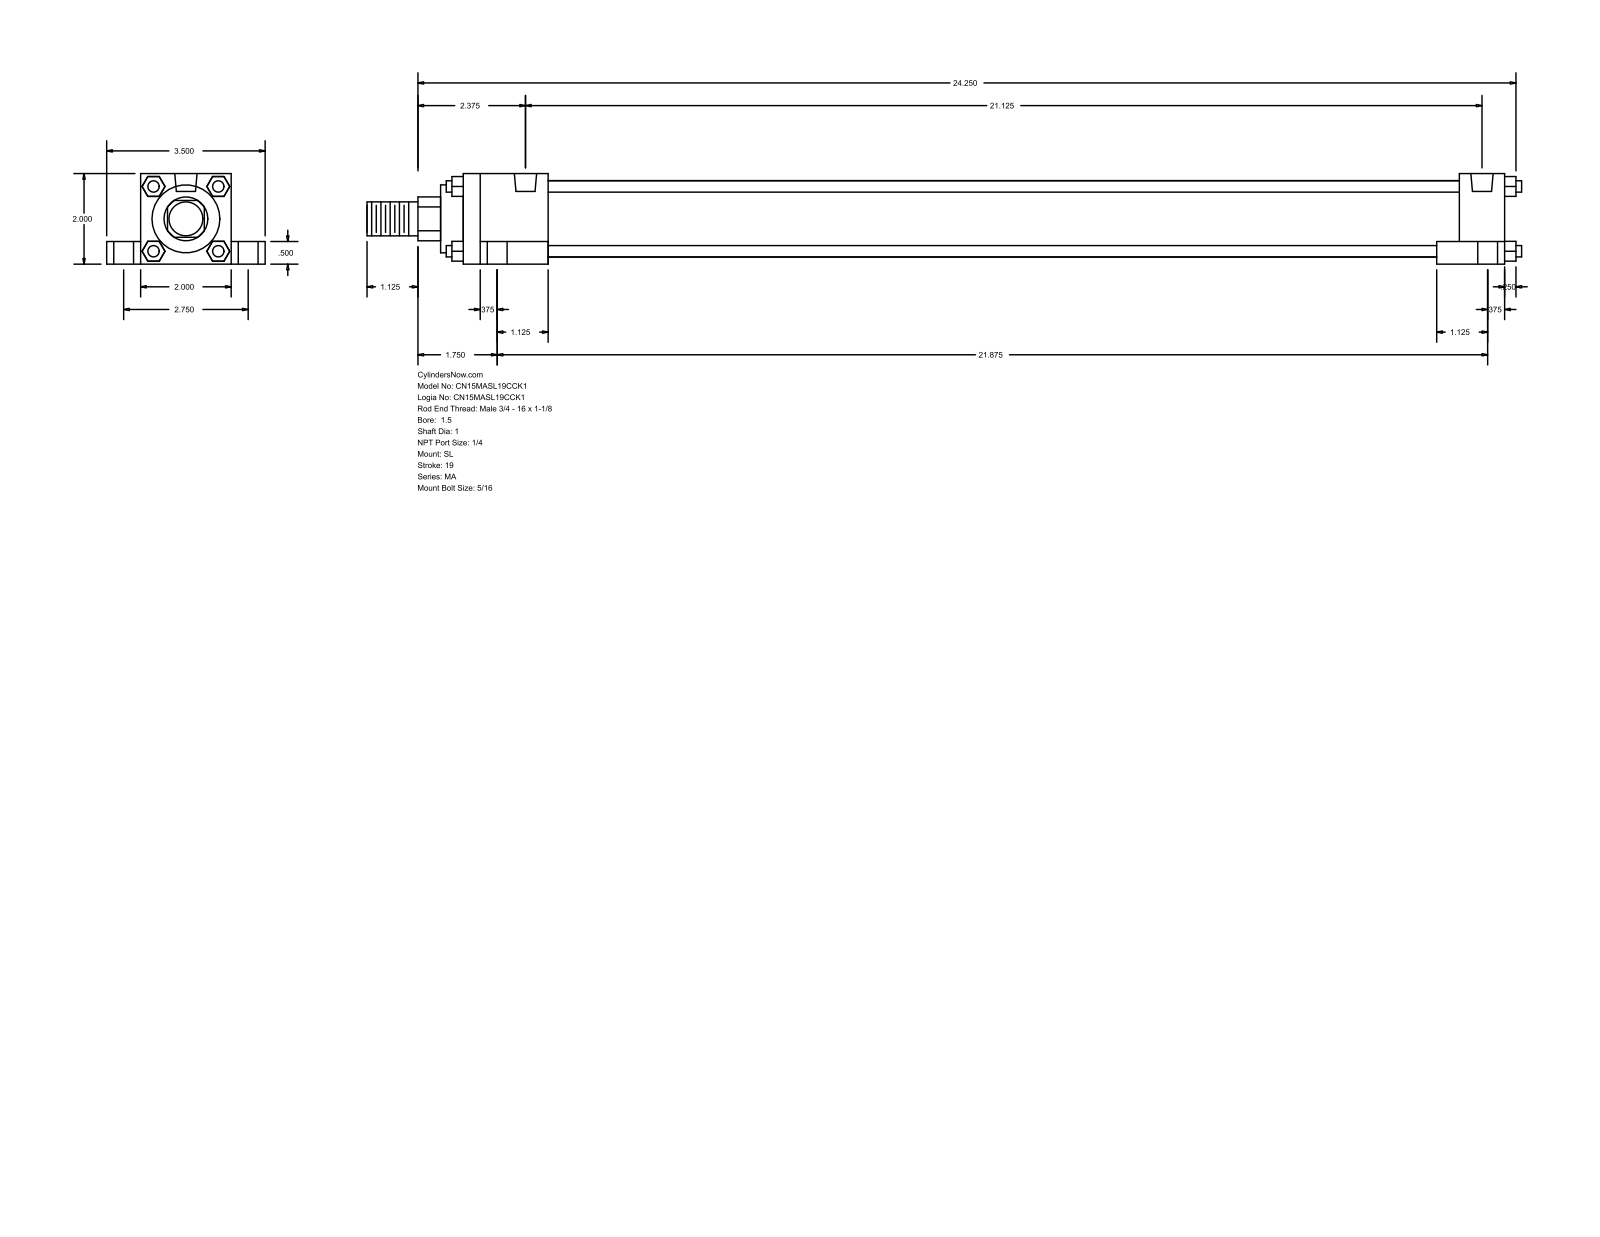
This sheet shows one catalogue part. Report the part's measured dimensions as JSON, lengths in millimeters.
{"part_name": "MA_SL__0150_1", "step_written_by": "GSSL Pune (CONFIG_CONTROL_DESIGN)", "units": "millimeters", "bodies": {"solids": 0, "faces": 148, "planar": 112, "cylindrical": 36, "other": 0}, "overall_size": [647.7, 88.9, 50.8], "round_holes": [[7.94, 4], [11.11, 4], [17.46, 4], [12.49, 2]], "round_bosses_or_shafts": [[6.35, 4], [42.93, 1], [38.1, 1], [25.4, 1], [19.05, 1]], "partial_cylinders_radius": [[12.29, 1]], "face_to_face_distances": [50.8, 12.7, 19.05, 69.85, 38.1, 9.52, 584.2, 25.4, 6.35, 558.8], "hole_center_spacings": [35.06, 38.36, 69.84, 536.57, 540.88, 553.55, 555.63, 560]}
